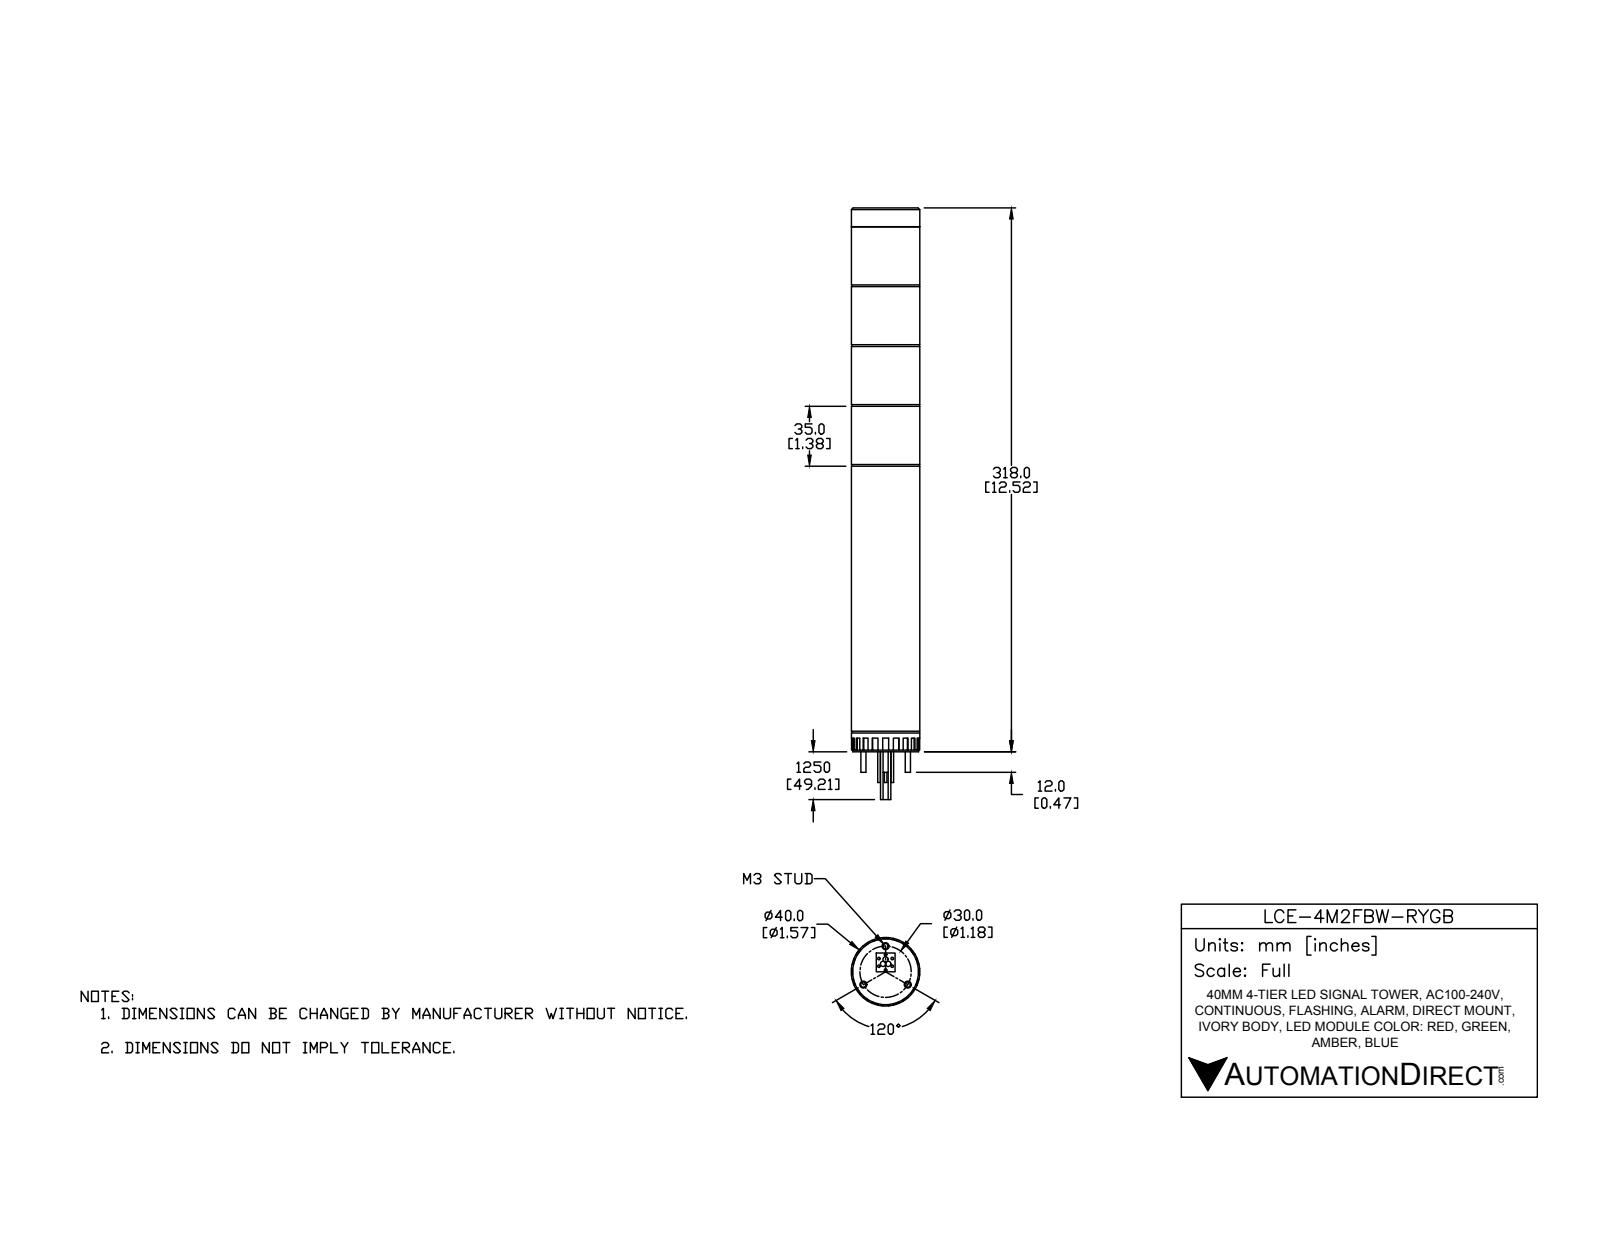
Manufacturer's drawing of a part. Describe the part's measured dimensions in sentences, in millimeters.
The part is named "LCE-4M2FBW-RYGB". Its 3-D file was written by "SolidWorks 2016 (AUTOMOTIVE_DESIGN)". It is 30 solids with 238 faces: 166 planar, 68 cylindrical and 4 other. Overall it measures 346 by 40 by 40 millimeters. Its volume is 398 757 cubic millimeters and its surface area 74 970 square millimeters. Round holes: 3 of diameter 4, 1 of diameter 8. Round bosses or shafts: 10 of diameter 1.5, 3 of diameter 3, 3 of diameter 2.5, 1 of diameter 40, 1 of diameter 39.5, 1 of diameter 38.5, 1 of diameter 5.5. The main face-to-face distances are 35, 1, 70, 34, 36, 105, 69, 71, 104, 156. The hole center spacings are 15, 25.98.
